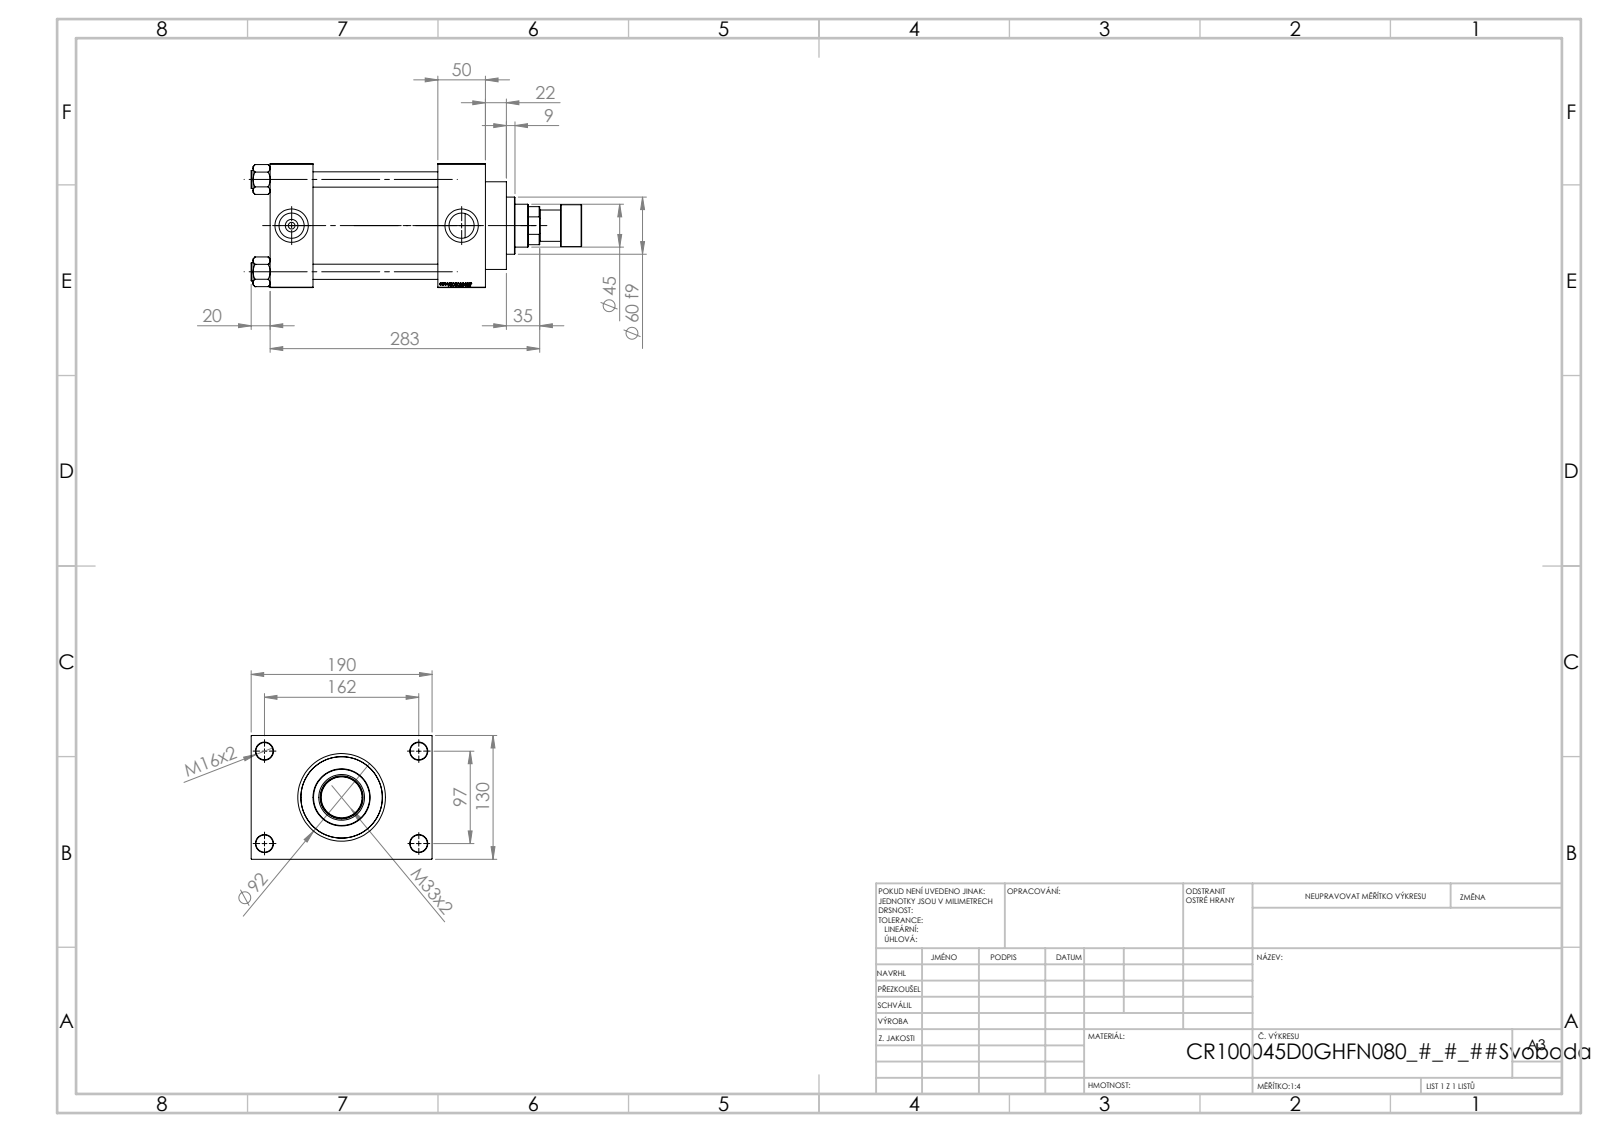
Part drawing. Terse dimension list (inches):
name: V215_VC_A; V215CR_D_TYCINKA; NUT_M5_D; V215CR_ROD_END_F (+2 more)
written by: SolidWorks 2019 (CONFIG_CONTROL_DESIGN)
unit: in
bodies: 12 solids, 1164 faces (548 planar, 92 cylindrical, 524 other)
size: 13.661 × 7.48 × 5.118
volume: 173.6 in³; area: 655.1 in²
holes: 4× ⌀0.63, 4× ⌀0.709, 2× ⌀0.276, 2× ⌀1.041, 2× ⌀1.378, 1× ⌀1.24, 1× ⌀1.772, 1× ⌀1.89, 1× ⌀2.992, 1× ⌀3.366, 1× ⌀3.937
bosses: 4× ⌀0.748, 1× ⌀4.173, 1× ⌀3.622, 1× ⌀2.362, 1× ⌀1.732, 1× ⌀1.299
face distances: 5.118, 1.772, 6.929, 5.157, 8.898, 7.126, 1.969, 1.181, 6.299, 3.15
hole spacings: 1.281, 2.698, 3.717, 3.815, 4.026, 5.096, 6.367, 3.819
